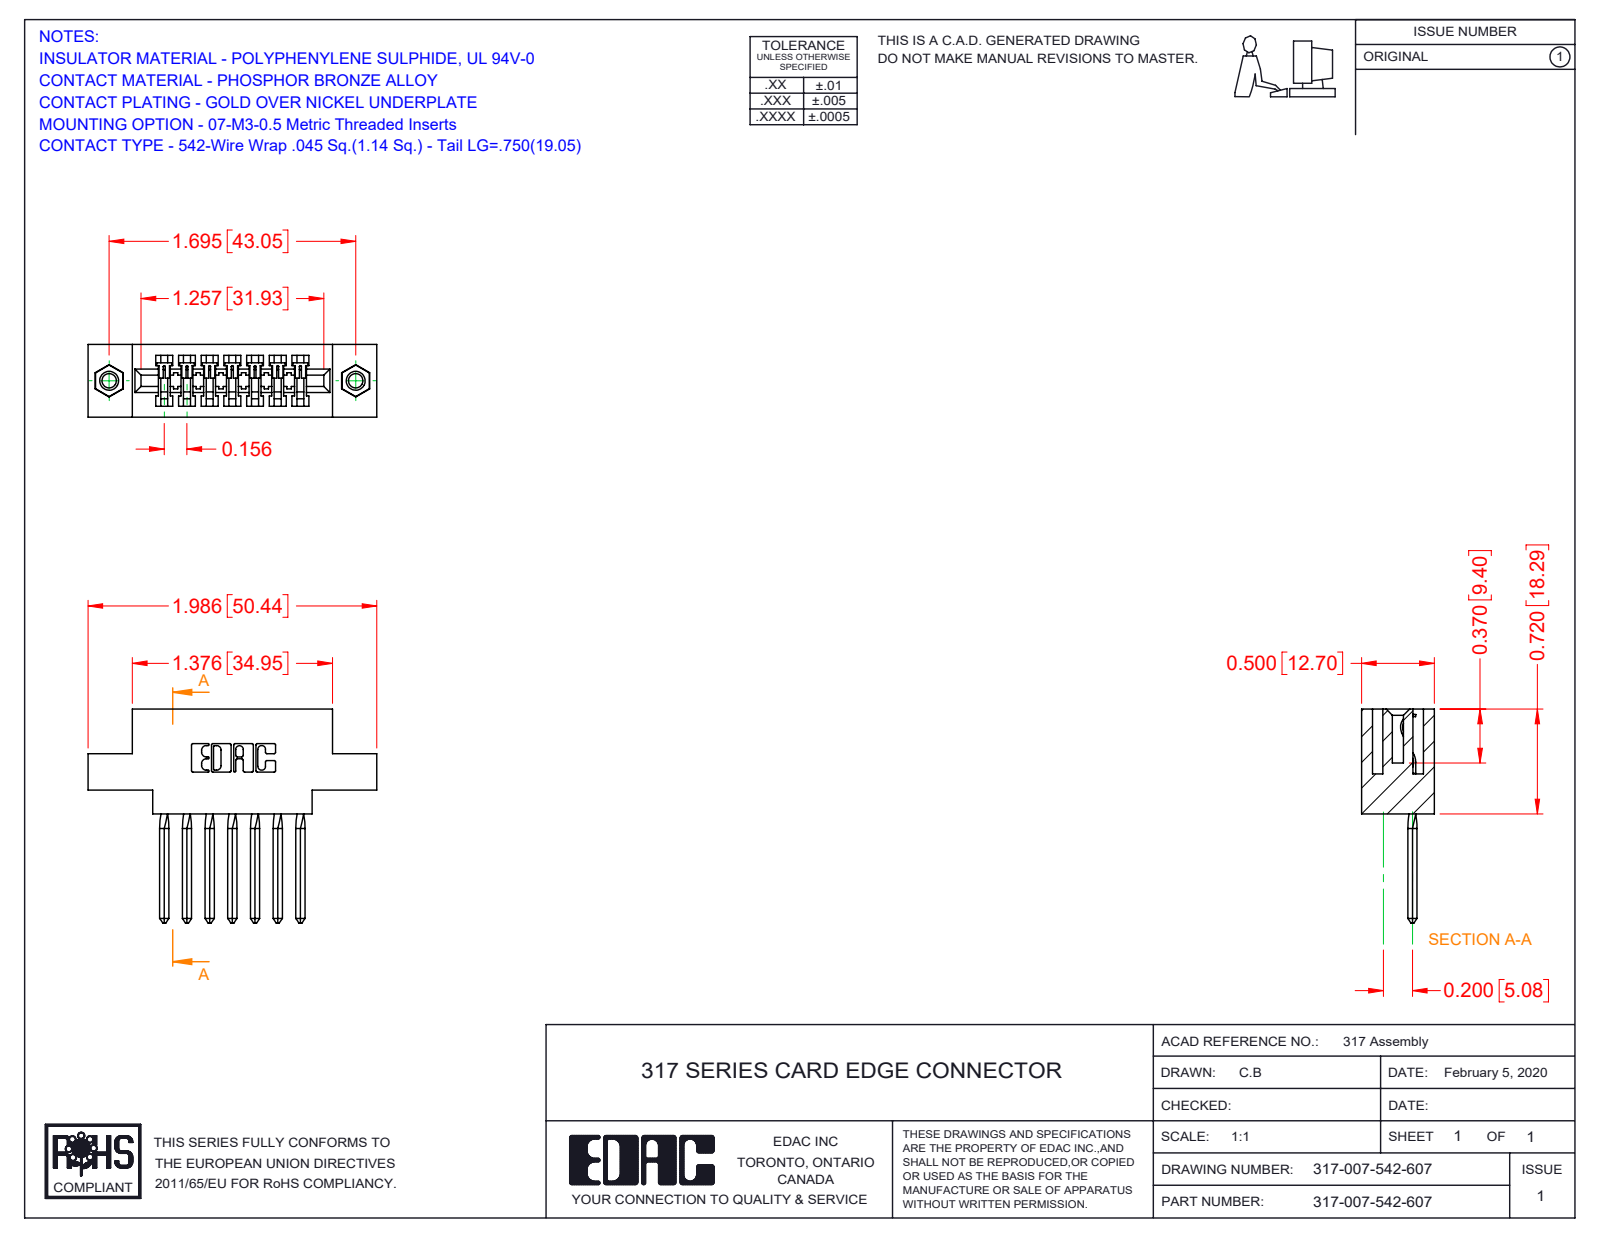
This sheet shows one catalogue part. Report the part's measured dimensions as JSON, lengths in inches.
{"part_name": "317-007-542-607; 317-290-003_542; 345-250-001_345-250-005-103; 317 Part_.156 Dia - TI", "step_written_by": "SolidWorks 2016 (CONFIG_CONTROL_DESIGN)", "units": "inches", "bodies": {"solids": 10, "faces": 687, "planar": 538, "cylindrical": 105, "other": 44}, "overall_size": [1.986, 1.47, 0.5], "volume_in3": 0.418, "surface_area_in2": 11.79, "round_holes": [[0.098, 2], [0.125, 2], [0.156, 2]], "round_bosses_or_shafts": [[0.155, 2]], "partial_cylinders_radius": [[0.01, 22], [0.006, 14], [0.007, 6], [0.031, 6], [0.026, 3], [0.074, 1], [0.089, 1], [0.1, 1]], "face_to_face_distances": [0.5, 0.075, 0.425, 0.11, 0.156, 0.065, 0.116, 0.22, 0.136, 0.163], "hole_center_spacings": [1.695]}
